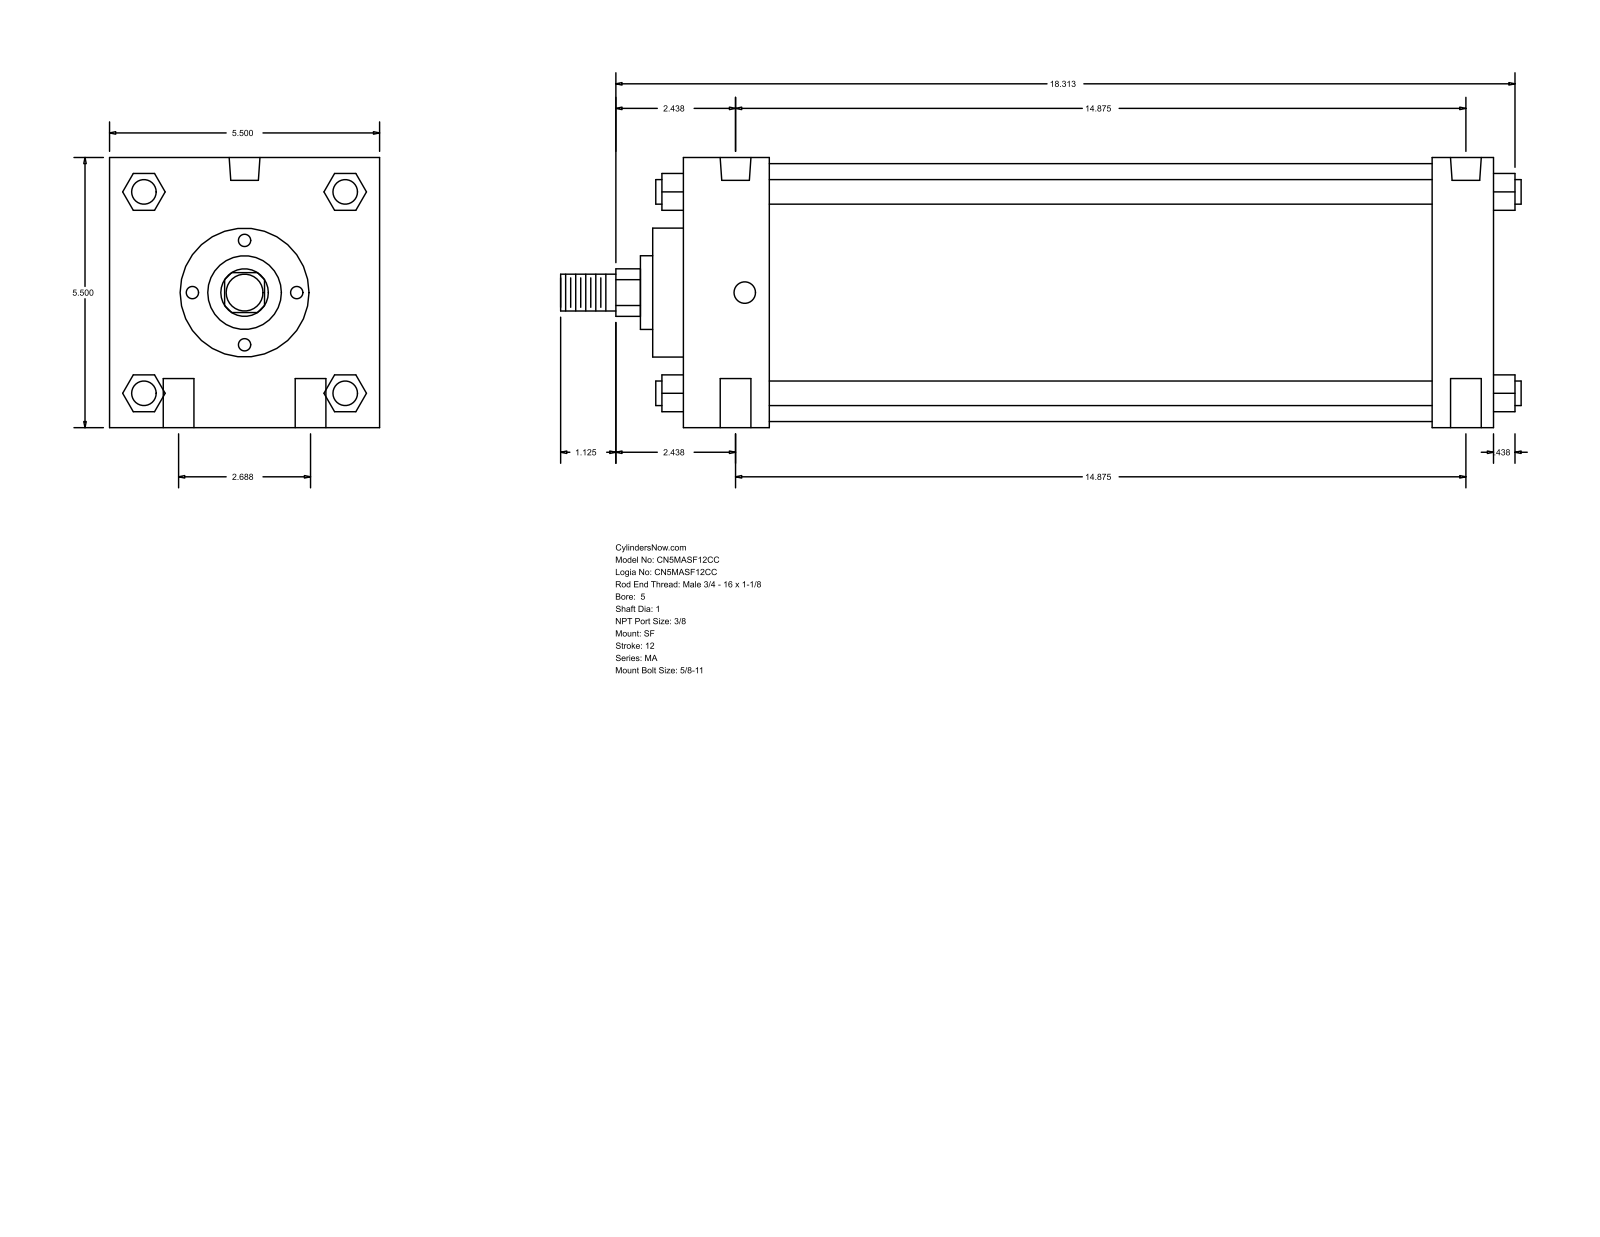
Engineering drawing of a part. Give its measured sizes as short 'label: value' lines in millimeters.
name: MA_SF__0500_1
written by: GSSL Pune (CONFIG_CONTROL_DESIGN)
unit: mm
bodies: 0 solids, 126 faces (95 planar, 31 cylindrical, 0 other)
size: 496.89 × 139.7 × 139.7
holes: 4× ⌀15.88, 2× ⌀11.11, 2× ⌀15.93
bosses: 4× ⌀12.7, 1× ⌀133.35, 1× ⌀66.67, 1× ⌀38.1, 1× ⌀25.4, 1× ⌀19.05
rounds: 1× R12.29
face distances: 139.7, 419.1, 44.46, 387.35, 342.89, 374.64, 31.75, 15.87, 60.33, 403.22
hole spacings: 34.13, 379.37, 377.83, 68.26, 383.95, 368.31
